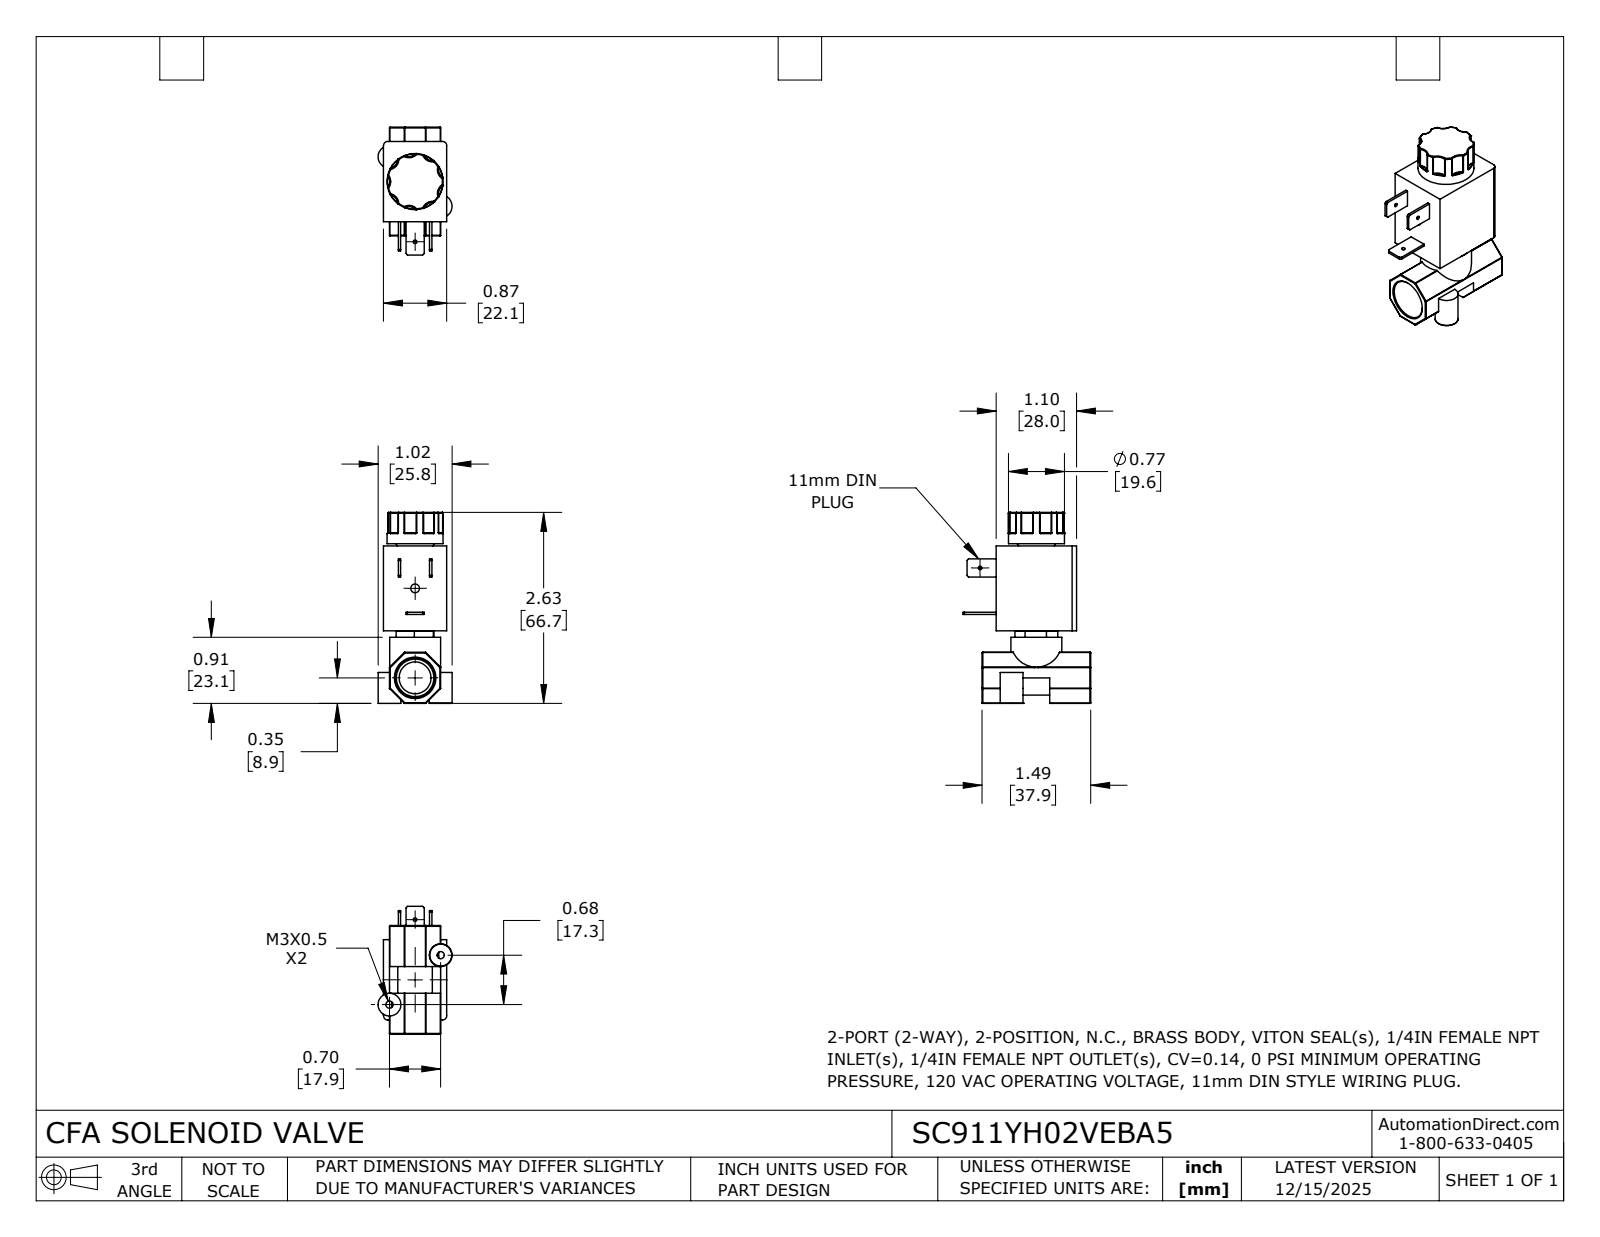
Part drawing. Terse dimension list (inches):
name: SC911YH02VEBA5
written by: SolidWorks 2024 (CONFIG_CONTROL_DESIGN)
unit: in
bodies: 1 solid, 314 faces (74 planar, 91 cylindrical, 149 other)
size: 2.625 × 1.757 × 1.017
volume: 1.798 in³; area: 16.13 in²
holes: 2× ⌀0.05, 2× ⌀0.1, 1× ⌀0.12, 1× ⌀0.438
bosses: 2× ⌀0.313, 1× ⌀0.77, 1× ⌀0.7
rounds: 42× R0.01, 7× R0.133, 2× R0.06, 2× R0.132, 1× R0.237, 1× R0.325
face distances: 0.87, 0.704, 1.104, 1.167, 0.083, 0.787, 0.46, 0.998, 2.165, 2.625
hole spacings: 0.602, 0.979, 1.22, 1.23
